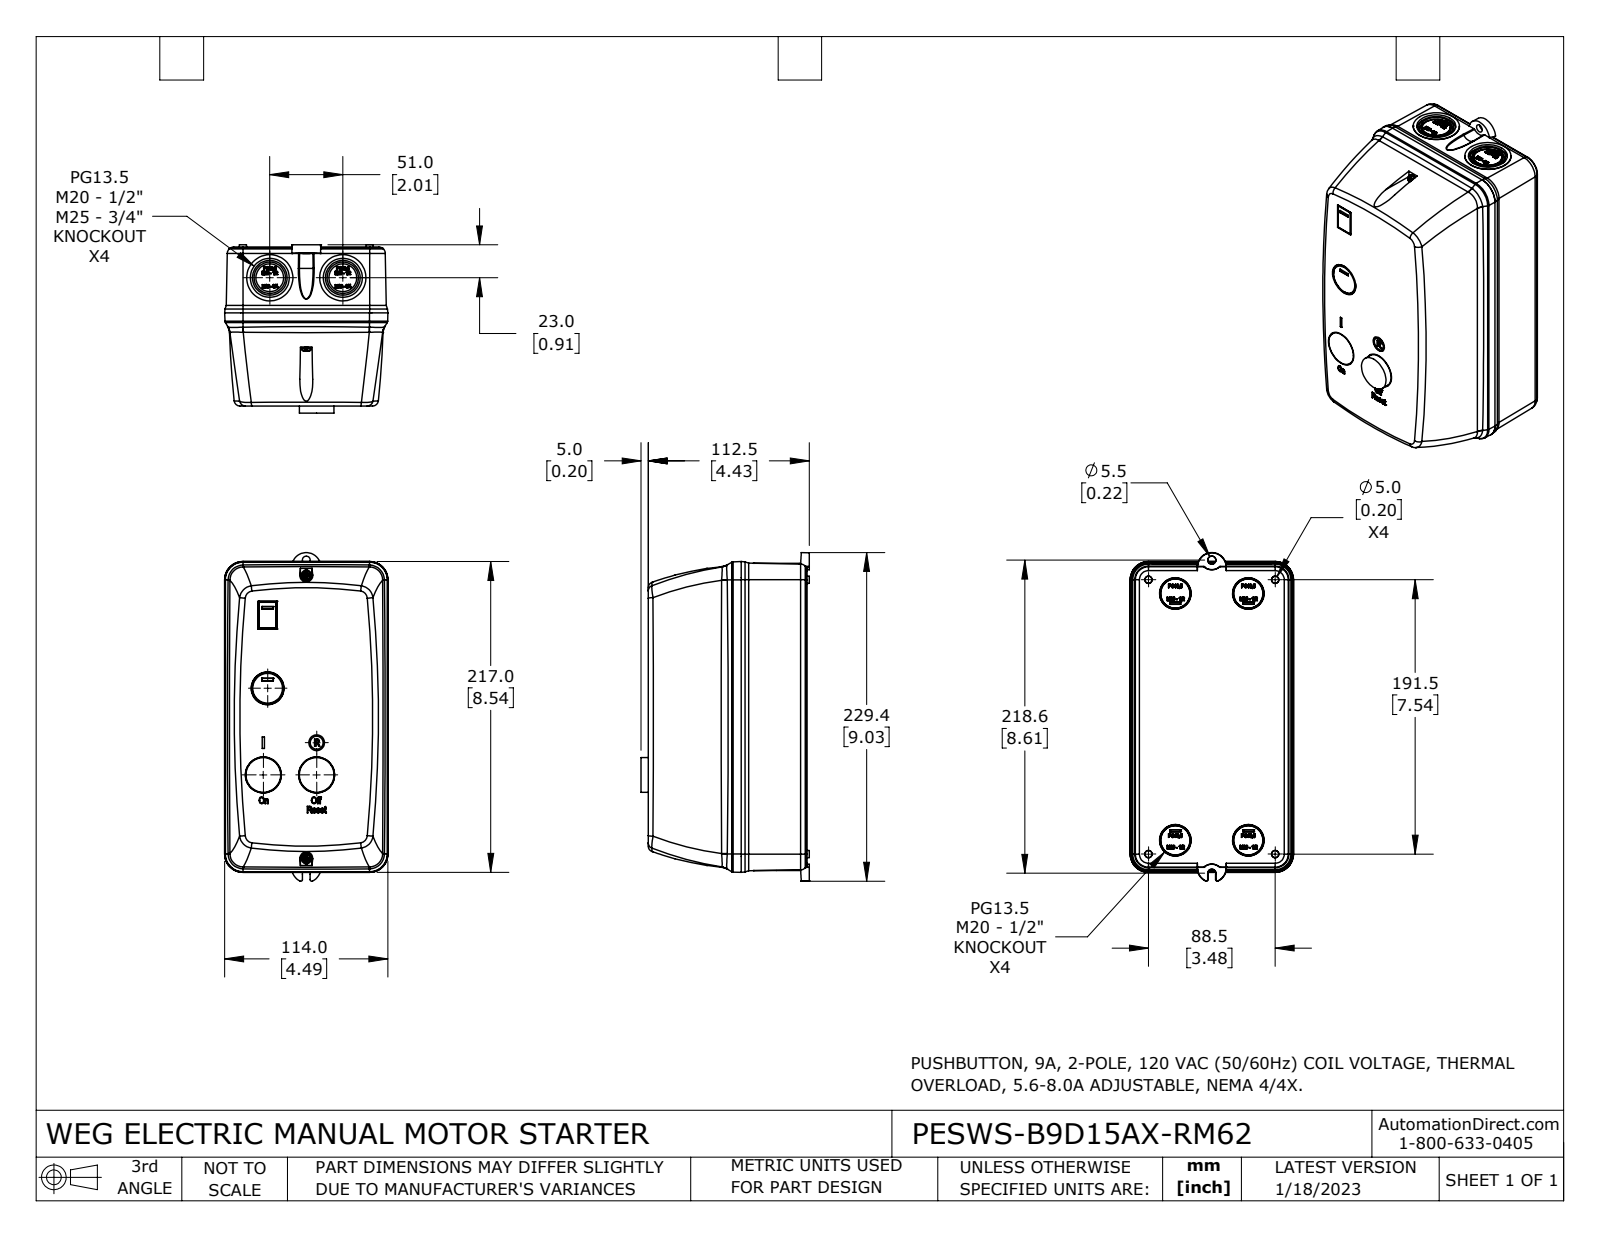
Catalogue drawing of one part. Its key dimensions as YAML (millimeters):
part_name: "PESWS-B9D15AX-RM62"
step_written_by: "SolidWorks 2021 (CONFIG_CONTROL_DESIGN)"
units: millimeters
bodies: {solids: 6, faces: 2195, planar: 1110, cylindrical: 92, other: 993}
overall_size: [229.44, 117.5, 114.01]
volume: 2457000
surface_area: 166196
round_holes:
  - {diameter: 4.4, count: 2}
  - {diameter: 21.91, count: 2}
  - {diameter: 27.24, count: 2}
  - {diameter: 5.5, count: 1}
  - {diameter: 11, count: 1}
round_bosses_or_shafts:
  - {diameter: 32.26, count: 2}
  - {diameter: 24.25, count: 2}
  - {diameter: 24.2, count: 2}
  - {diameter: 19.37, count: 2}
  - {diameter: 7, count: 2}
  - {diameter: 3, count: 2}
  - {diameter: 9, count: 1}
partial_cylinders:
  - {radius: 2, count: 4}
  - {radius: 4.61, count: 4}
  - {radius: 9.54, count: 4}
  - {radius: 6.54, count: 2}
  - {radius: 7.54, count: 2}
  - {radius: 2.08, count: 1}
  - {radius: 2.17, count: 1}
  - {radius: 2.75, count: 1}
face_to_face_distances: [46, 65, 111, 0.5, 110.5, 45.5, 110, 1, 109.5, 64]
hole_center_spacings: [10.5, 51, 81.32, 117.22, 127.71, 198, 208.5]
